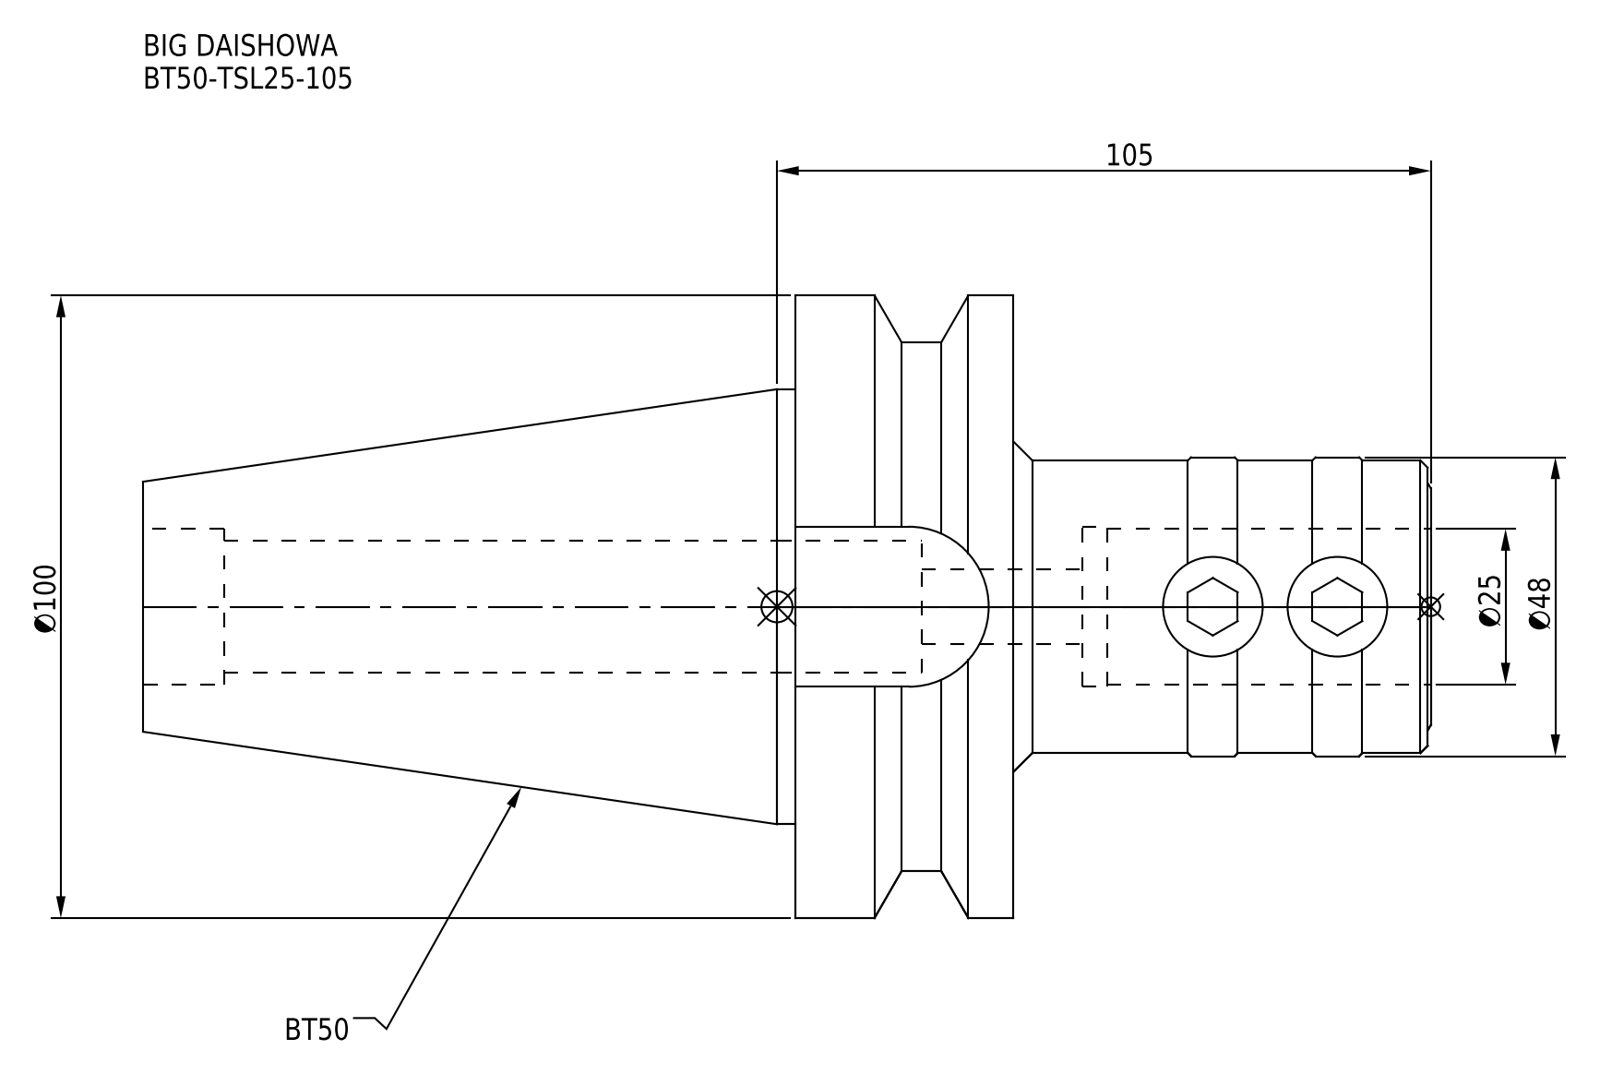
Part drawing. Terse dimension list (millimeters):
name: BT50-TSL25-105
written by: CREO PARAMETRIC BY PTC INC, 2016380 (AUTOMOTIVE_DESIGN)
unit: mm
bodies: 1 solid, 67 faces (15 planar, 32 cylindrical, 20 other)
size: 206.8 × 100 × 100
volume: 535 291 mm³; area: 68 472 mm²
holes: 1× ⌀12, 1× ⌀21.2, 1× ⌀25, 1× ⌀25.6
bosses: 1× ⌀100, 1× ⌀85, 1× ⌀69.85, 1× ⌀48, 1× ⌀47
rounds: 1× R12.85
face distances: 35, 139.8, 104.8, 70.8, 67, 102, 206.8, 25.7, 56, 11
